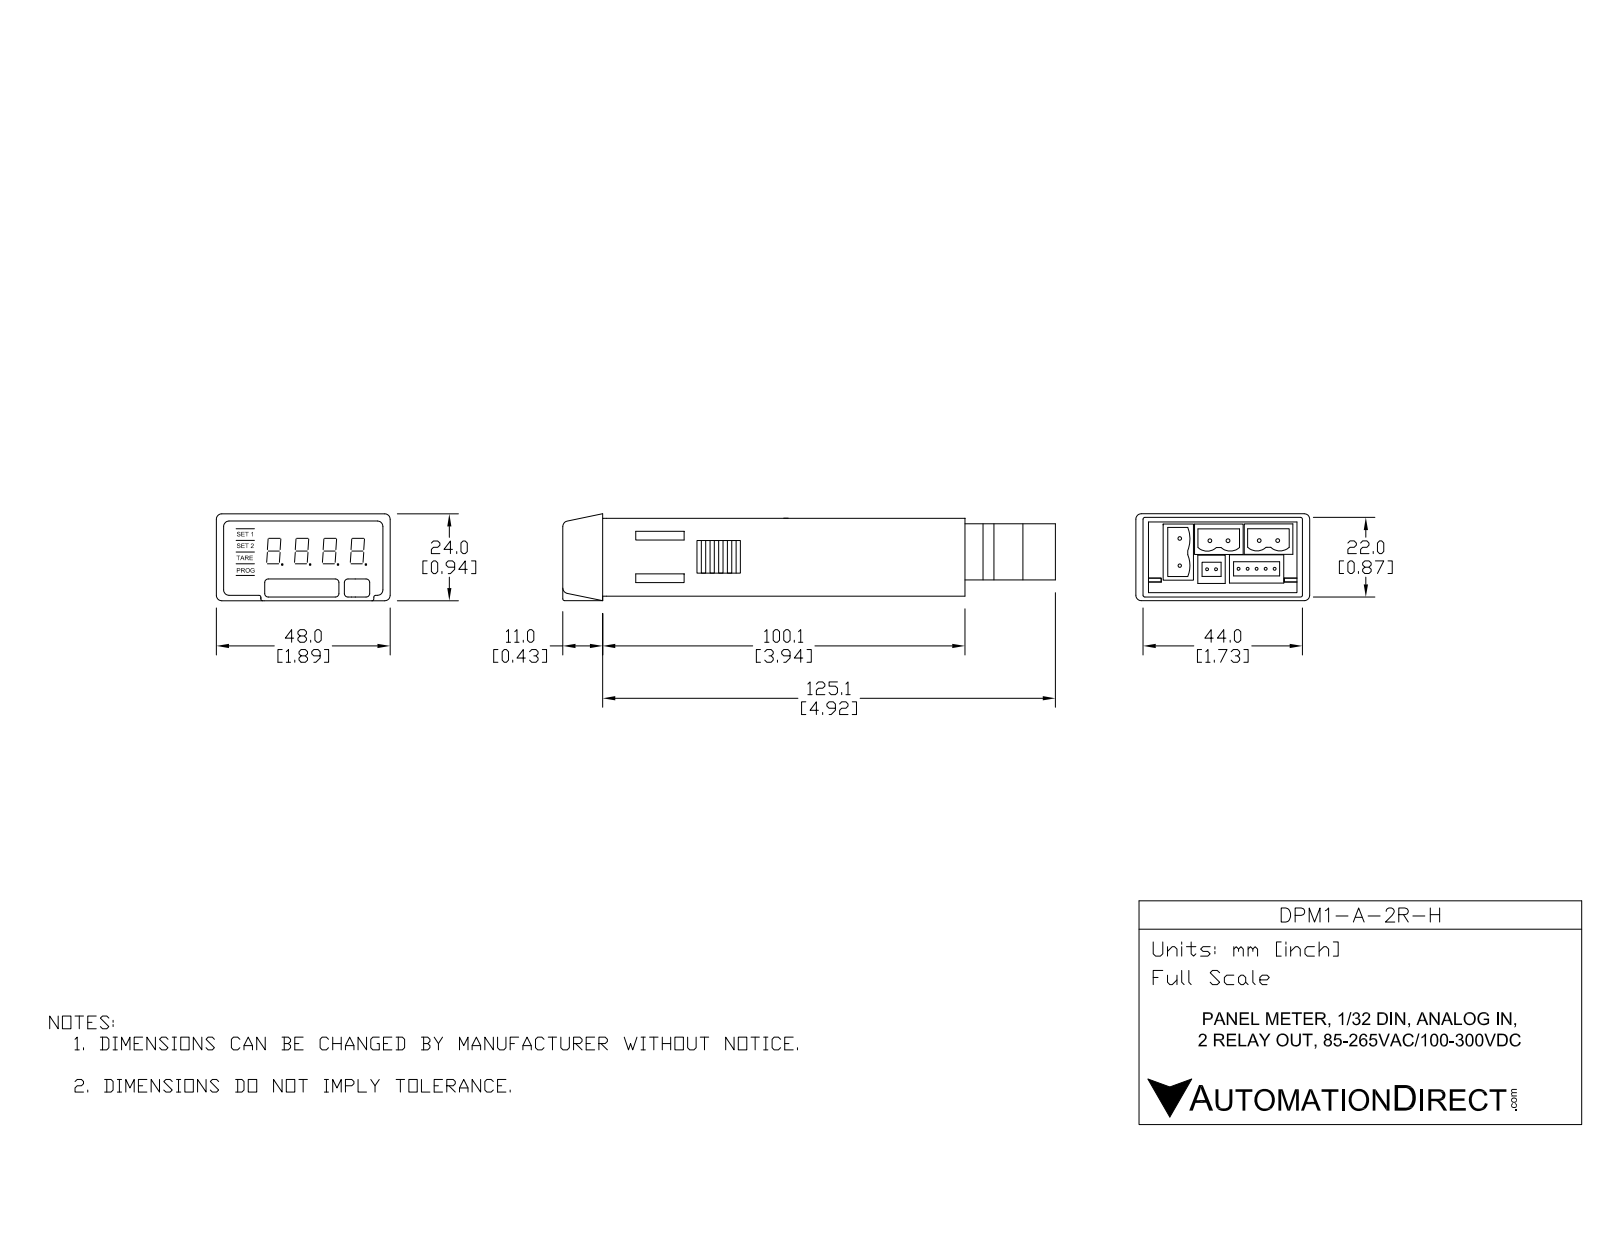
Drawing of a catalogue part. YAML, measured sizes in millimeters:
part_name: "DPM1-A-2R-H"
step_written_by: "SolidWorks 2017 (AUTOMOTIVE_DESIGN)"
units: millimeters
bodies: {solids: 6, faces: 1467, planar: 1124, cylindrical: 167, other: 176}
overall_size: [136, 48, 24.9]
volume: 42160
surface_area: 39160
round_holes:
  - {diameter: 1, count: 7}
  - {diameter: 2, count: 7}
  - {diameter: 2, count: 6}
  - {diameter: 3, count: 6}
  - {diameter: 3.9, count: 6}
partial_cylinders:
  - {radius: 0.3, count: 14}
  - {radius: 0.4, count: 14}
  - {radius: 0.5, count: 14}
  - {radius: 1.8, count: 7}
  - {radius: 1.8, count: 7}
  - {radius: 3.1, count: 6}
  - {radius: 1, count: 4}
  - {radius: 0.6, count: 2}
face_to_face_distances: [1.5, 20.5, 22, 19, 42.5, 44, 41, 1.3, 11, 109.6]
hole_center_spacings: [13.7, 3.5, 5, 5, 5.1, 5.1, 7, 7.3]
